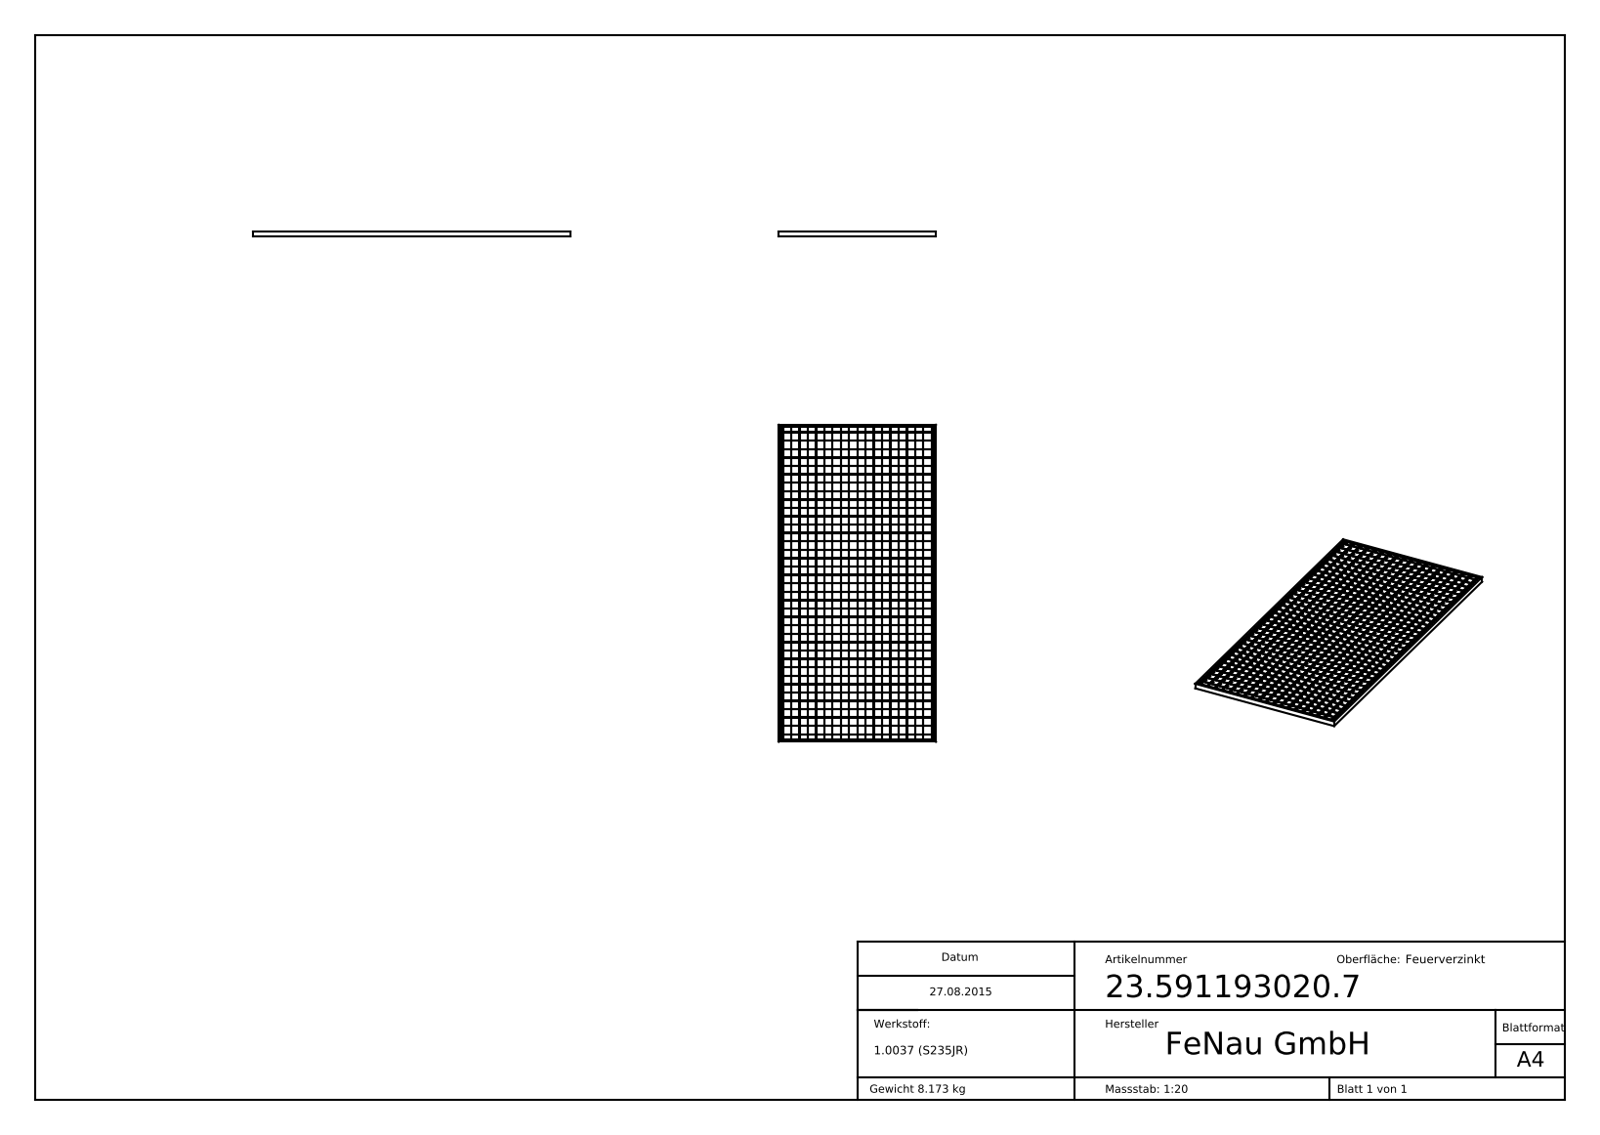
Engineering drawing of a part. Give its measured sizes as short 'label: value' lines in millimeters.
name: 23-591193020-7
written by: SolidWorks 2015 (CONFIG_CONTROL_DESIGN)
unit: mm
bodies: 1 solid, 2558 faces (2558 planar, 0 cylindrical, 0 other)
size: 1190 × 590 × 20
volume: 1 048 000 mm³; area: 1 582 000 mm²
face distances: 63, 31.5, 94.5, 126, 157.5, 31, 189, 220.5, 252, 62
